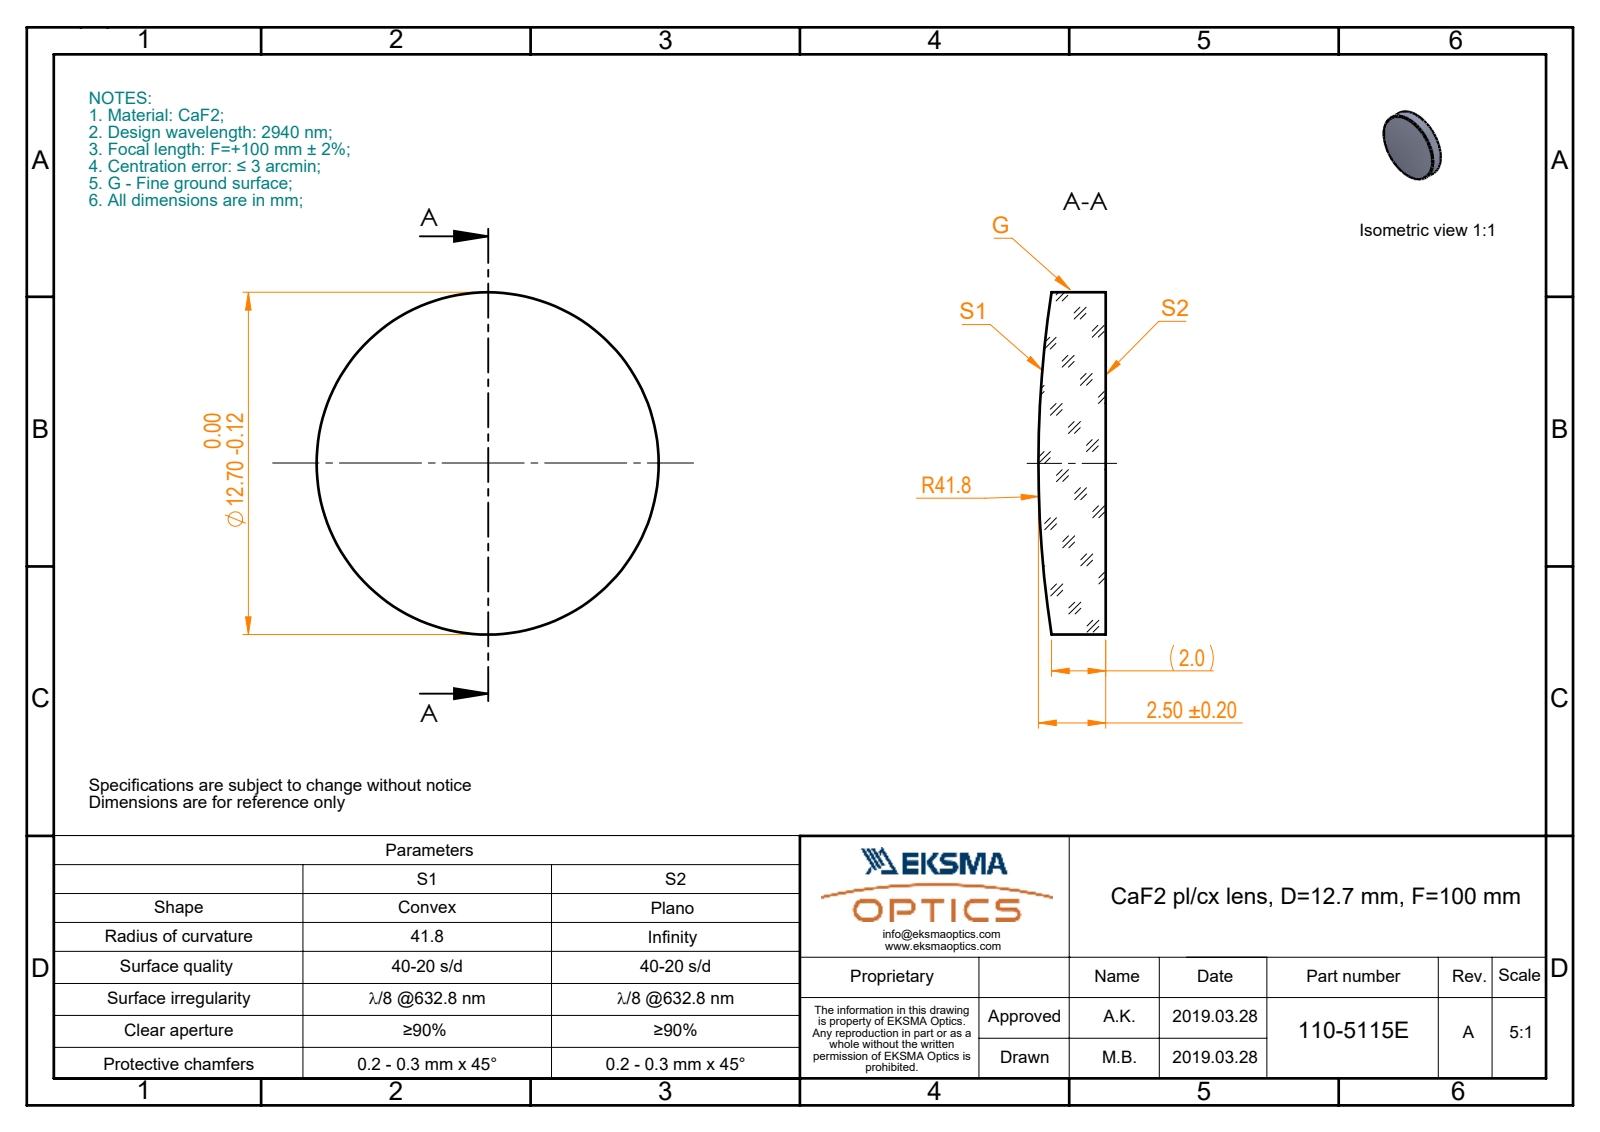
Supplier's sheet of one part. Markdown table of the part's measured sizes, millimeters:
| quantity | value |
| --- | --- |
| part name | 110-5115E CaF2 pl-cx 12.7 F100 |
| STEP written by | SolidWorks 2017 (CONFIG_CONTROL_DESIGN) |
| units | millimeters |
| bodies | 1 solid, 5 faces (1 planar, 2 cylindrical, 2 other) |
| overall size | 12.7 × 12.7 × 2.5 |
| volume | 286 mm³ |
| surface area | 334 mm² |
| round bosses / shafts (diameter × count) | 12.7 × 1 |
